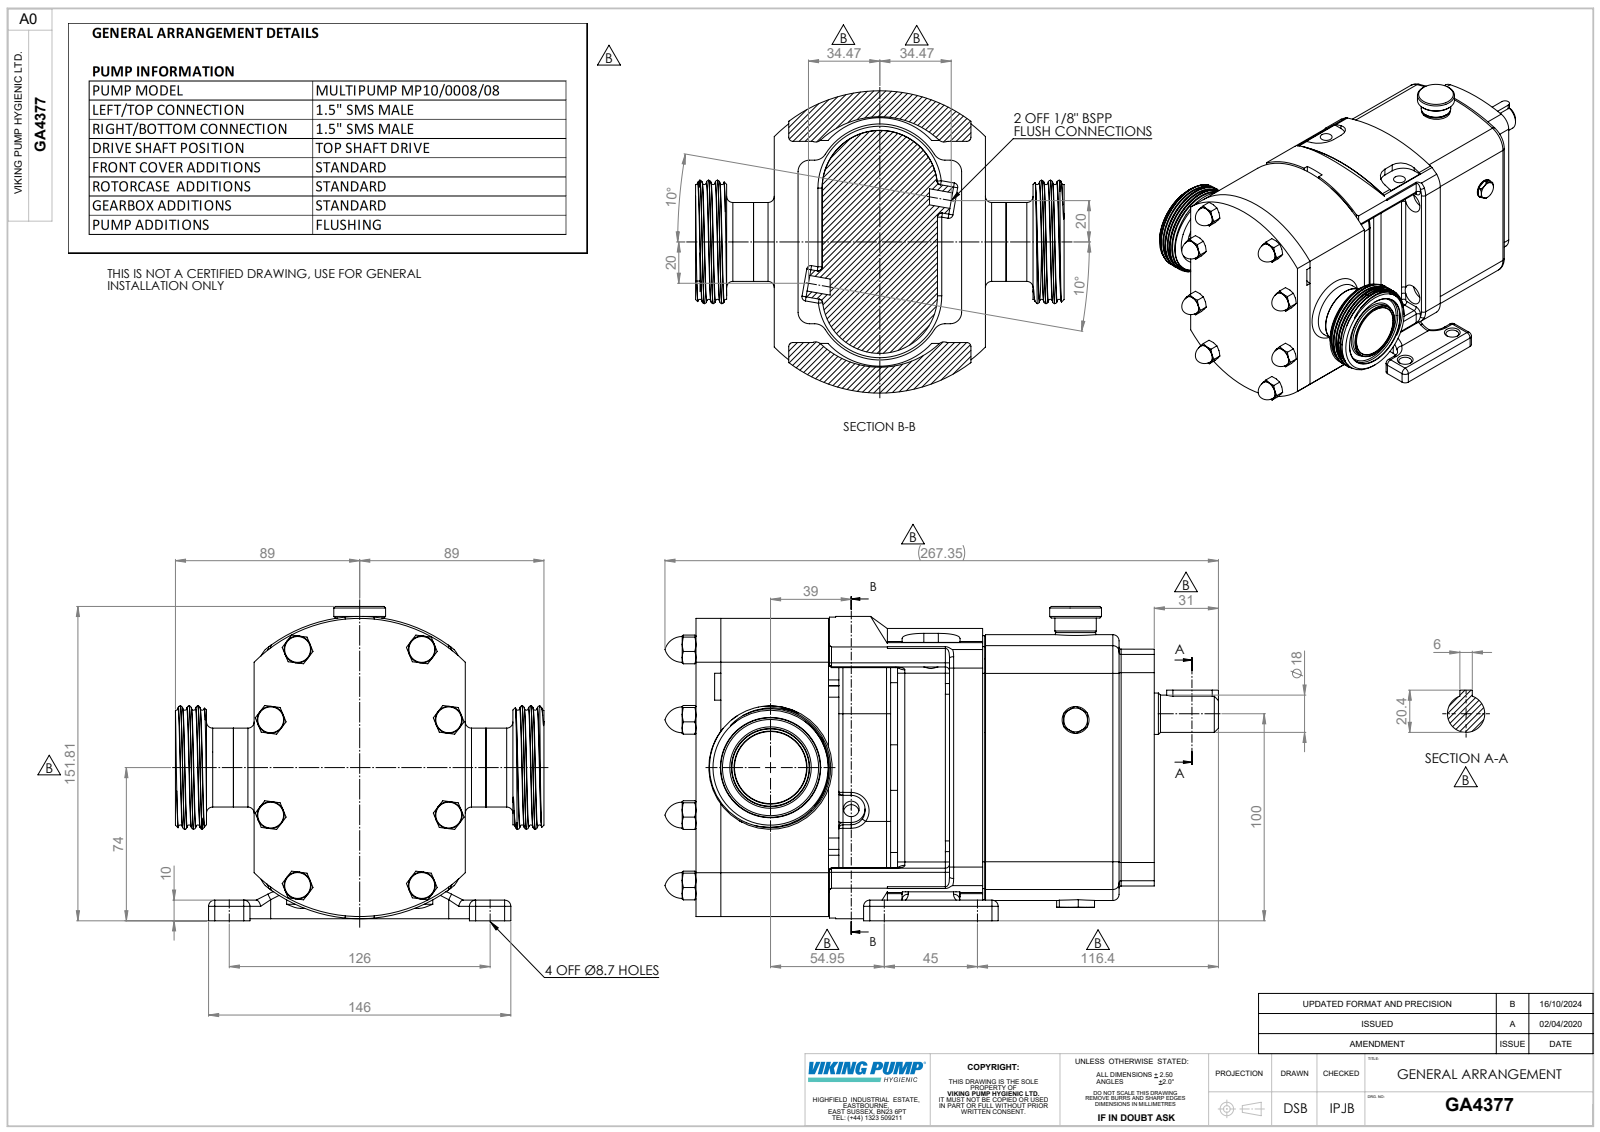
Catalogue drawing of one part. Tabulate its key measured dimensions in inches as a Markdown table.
| quantity | value |
| --- | --- |
| part name | Copy of Z94-5101-22^GA4377_Z94-5101-22; GA4377; Copy of CP10-0008-08 H T^GA4377 |
| STEP written by | SolidWorks 2023 (AUTOMOTIVE_DESIGN) |
| units | inches |
| bodies | 3 solids, 806 faces (258 planar, 234 cylindrical, 314 other) |
| overall size | 10.526 × 7.008 × 5.977 |
| volume | 152.6 in³ |
| surface area | 309.8 in² |
| round holes (diameter × count) | 0.343 × 4, 0.551 × 4, 0.3 × 2, 0.315 × 2, 0.887 × 1, 1.372 × 1, 1.892 × 1 |
| round bosses / shafts (diameter × count) | 1.181 × 2, 2.346 × 1, 1.5 × 1, 1.486 × 1, 0.985 × 1, 0.787 × 1, 0.787 × 1, 0.768 × 1 |
| partial cylindrical surfaces (radius × count) | 0.079 × 30, 0.118 × 26, 0.531 × 12, 0.413 × 8, 0.138 × 6, 0.217 × 4, 0.236 × 4, 0.354 × 4 |
| main face-to-face distances | 0.197, 8.715, 4.882, 4.016, 3.819, 0.197, 3.622, 3.819, 1.181, 3.833 |
| hole center spacings | 1.414, 3.959, 1.772, 2.992, 3.032, 4.26, 4.961, 5.267 |
